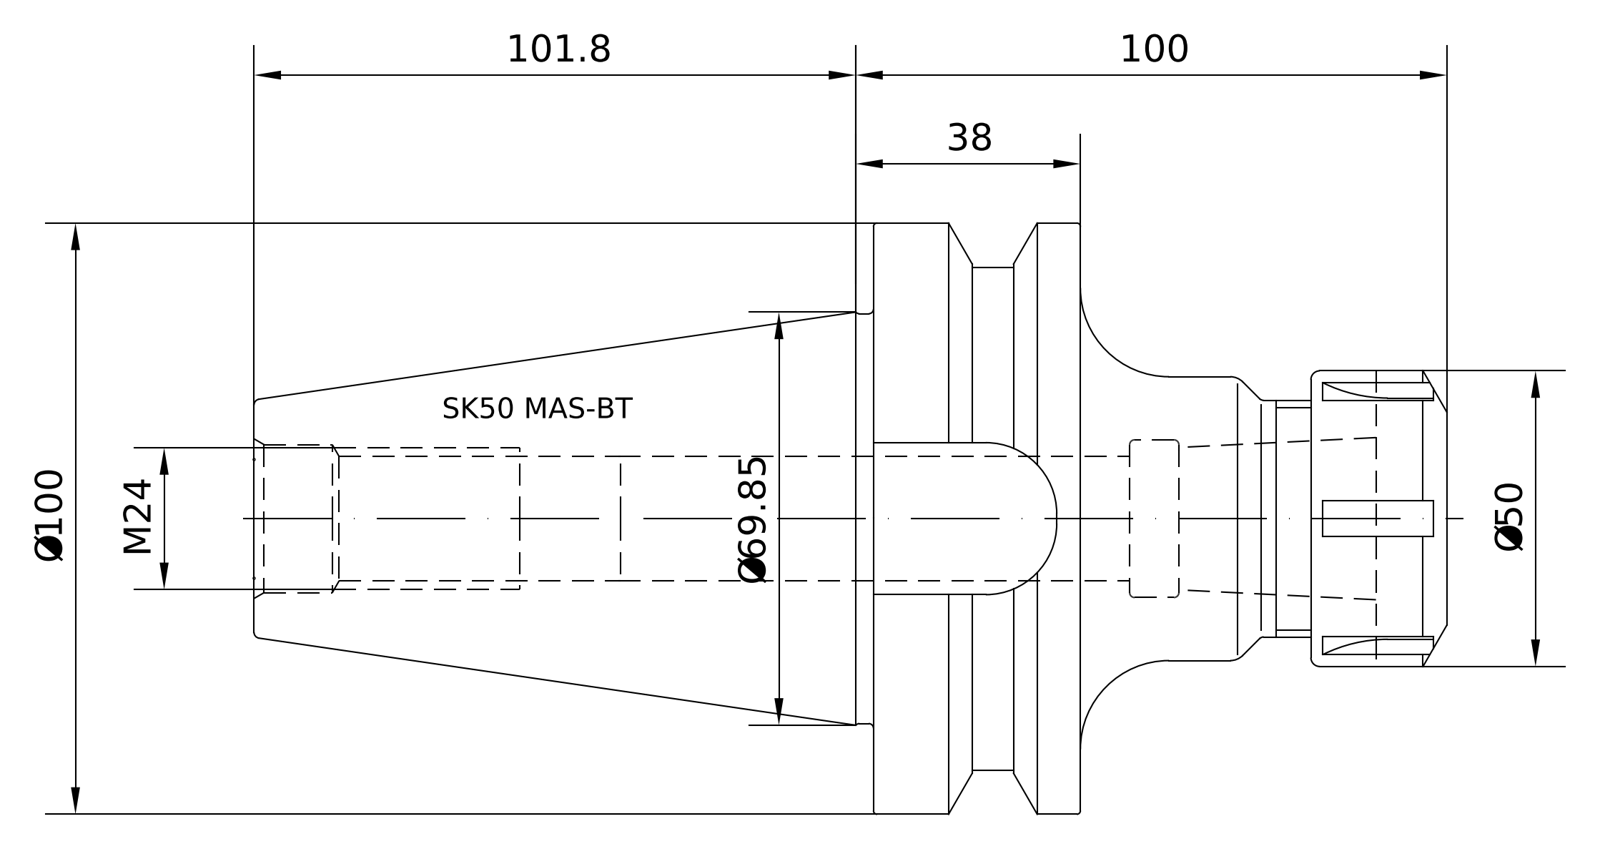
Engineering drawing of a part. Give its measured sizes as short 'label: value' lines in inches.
name: 50-521-32; 83-912-32; 50-521-32_ASM
written by: PRO/ENGINEER BY PARAMETRIC TECHNOLOGY CORPORATION, 2010430 (CONFIG_CONTROL_DESIGN)
unit: in
bodies: 2 solids, 146 faces (52 planar, 32 cylindrical, 62 other)
size: 7.945 × 3.936 × 3.936
volume: 34.6 in³; area: 106.2 in²
holes: 1× ⌀0.817, 1× ⌀0.925, 1× ⌀0.985, 1× ⌀1.012
bosses: 1× ⌀3.936, 1× ⌀3.337, 1× ⌀2.722, 1× ⌀1.969, 1× ⌀1.89, 1× ⌀1.575, 1× ⌀0.945
rounds: 6× R0.106, 1× R0.508
face distances: 1.378, 2.933, 1.555, 3.819, 2.441, 0.886, 2.772, 4.126, 5.504, 7.059
